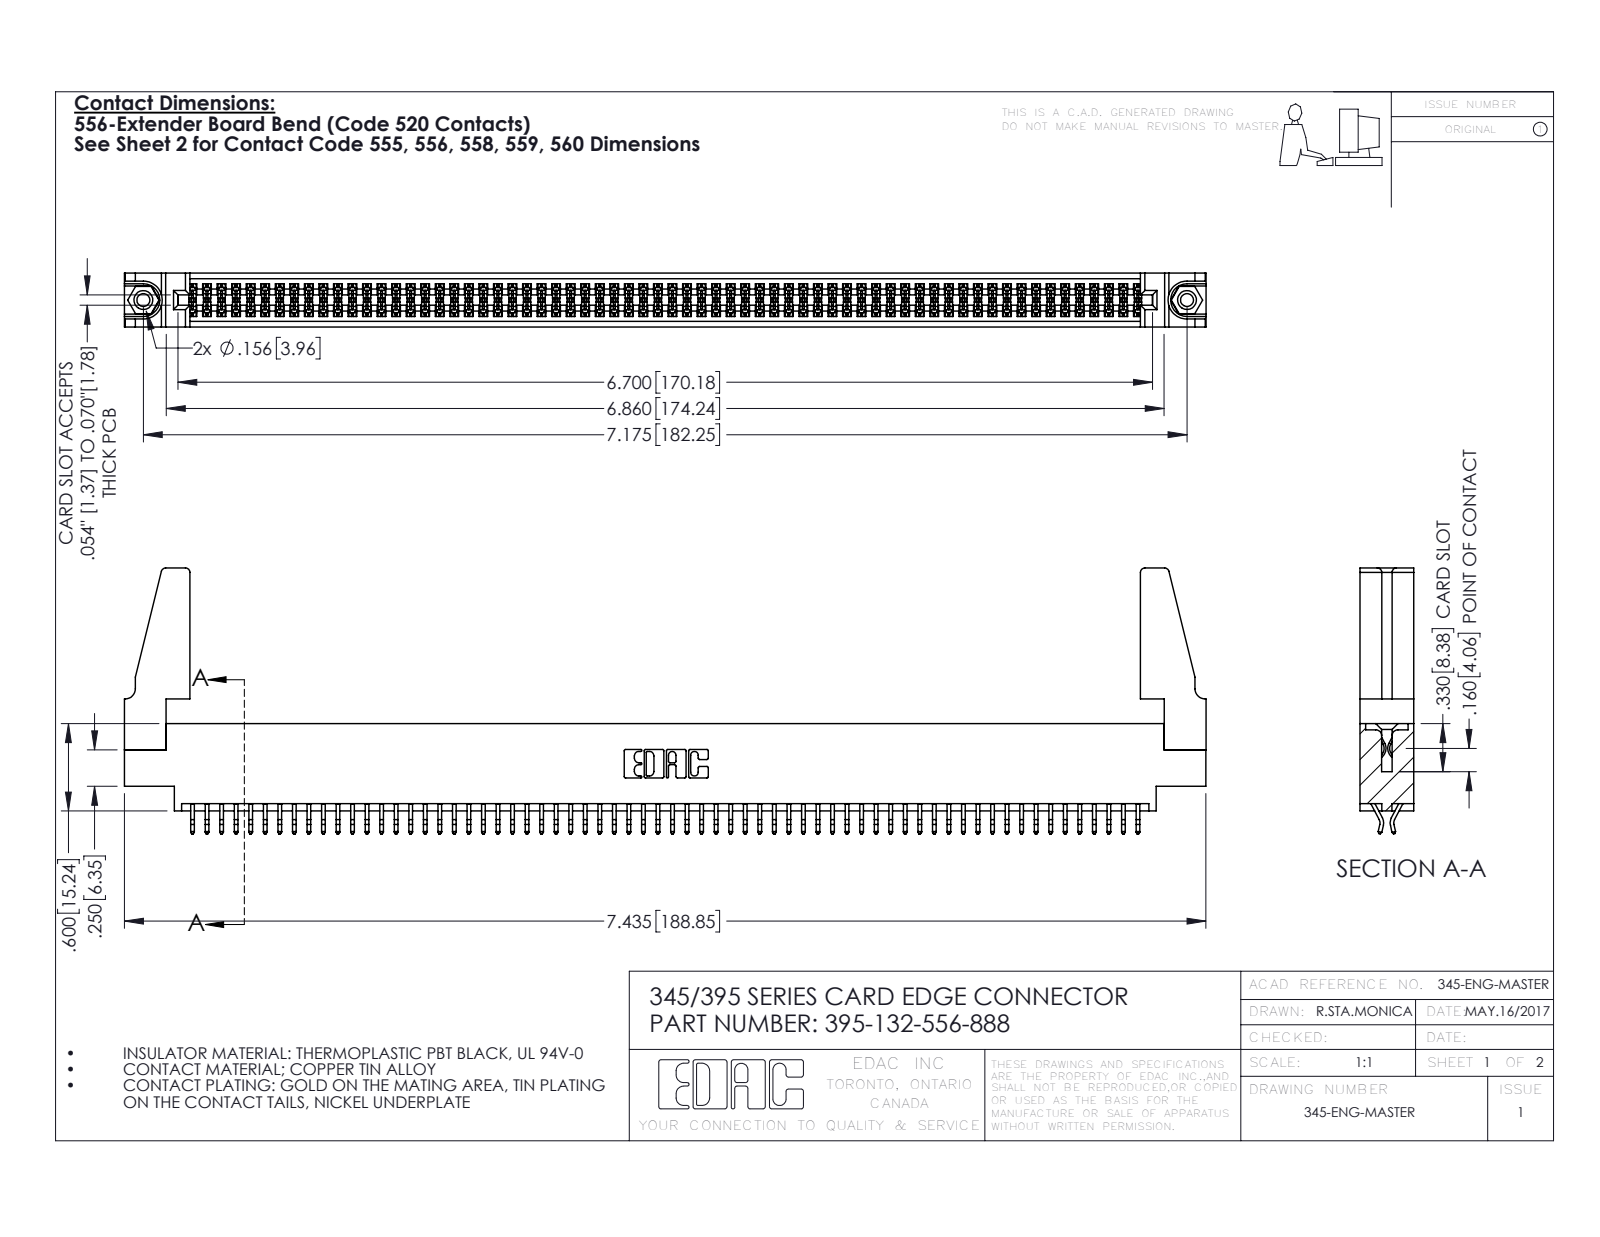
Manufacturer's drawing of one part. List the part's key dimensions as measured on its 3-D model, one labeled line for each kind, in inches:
Part name (STEP PRODUCT): 345-250-001_345-250-001-102; 345 Part_0.170 Offset - 0.156 Dia-TH; 345-220-078_345-220-088; 395-132-556-888 (+1 more)
STEP written by: SolidWorks 2016 (CONFIG_CONTROL_DESIGN)
Units: inches
Bodies: 137 solids, 7646 faces (5040 planar, 2590 cylindrical, 16 other)
Overall size (bounding box): 7.436 × 1.827 × 0.37
Volume: 1.324 in³ · Surface area: 47.88 in²
Round holes (diameter × count): ⌀0.089 ×2, ⌀0.125 ×2, ⌀0.156 ×2, ⌀0.064 ×1
Round bosses / shafts (diameter × count): ⌀0.155 ×2
Partial cylindrical surfaces — rounded edges, fillets, slot ends (radius × count): R0.006 ×198, R0.01 ×22, R0.03 ×8, R0.007 ×6, R0.031 ×6, R0.026 ×3, R0.01 ×2, R0.014 ×2
Main face-to-face distances: 0.072, 0.298, 0.37, 0.025, 0.098, 0.272, 0.2, 0.225, 0.175, 0.149
Hole centre spacings: 0.27, 6.939, 7.175
